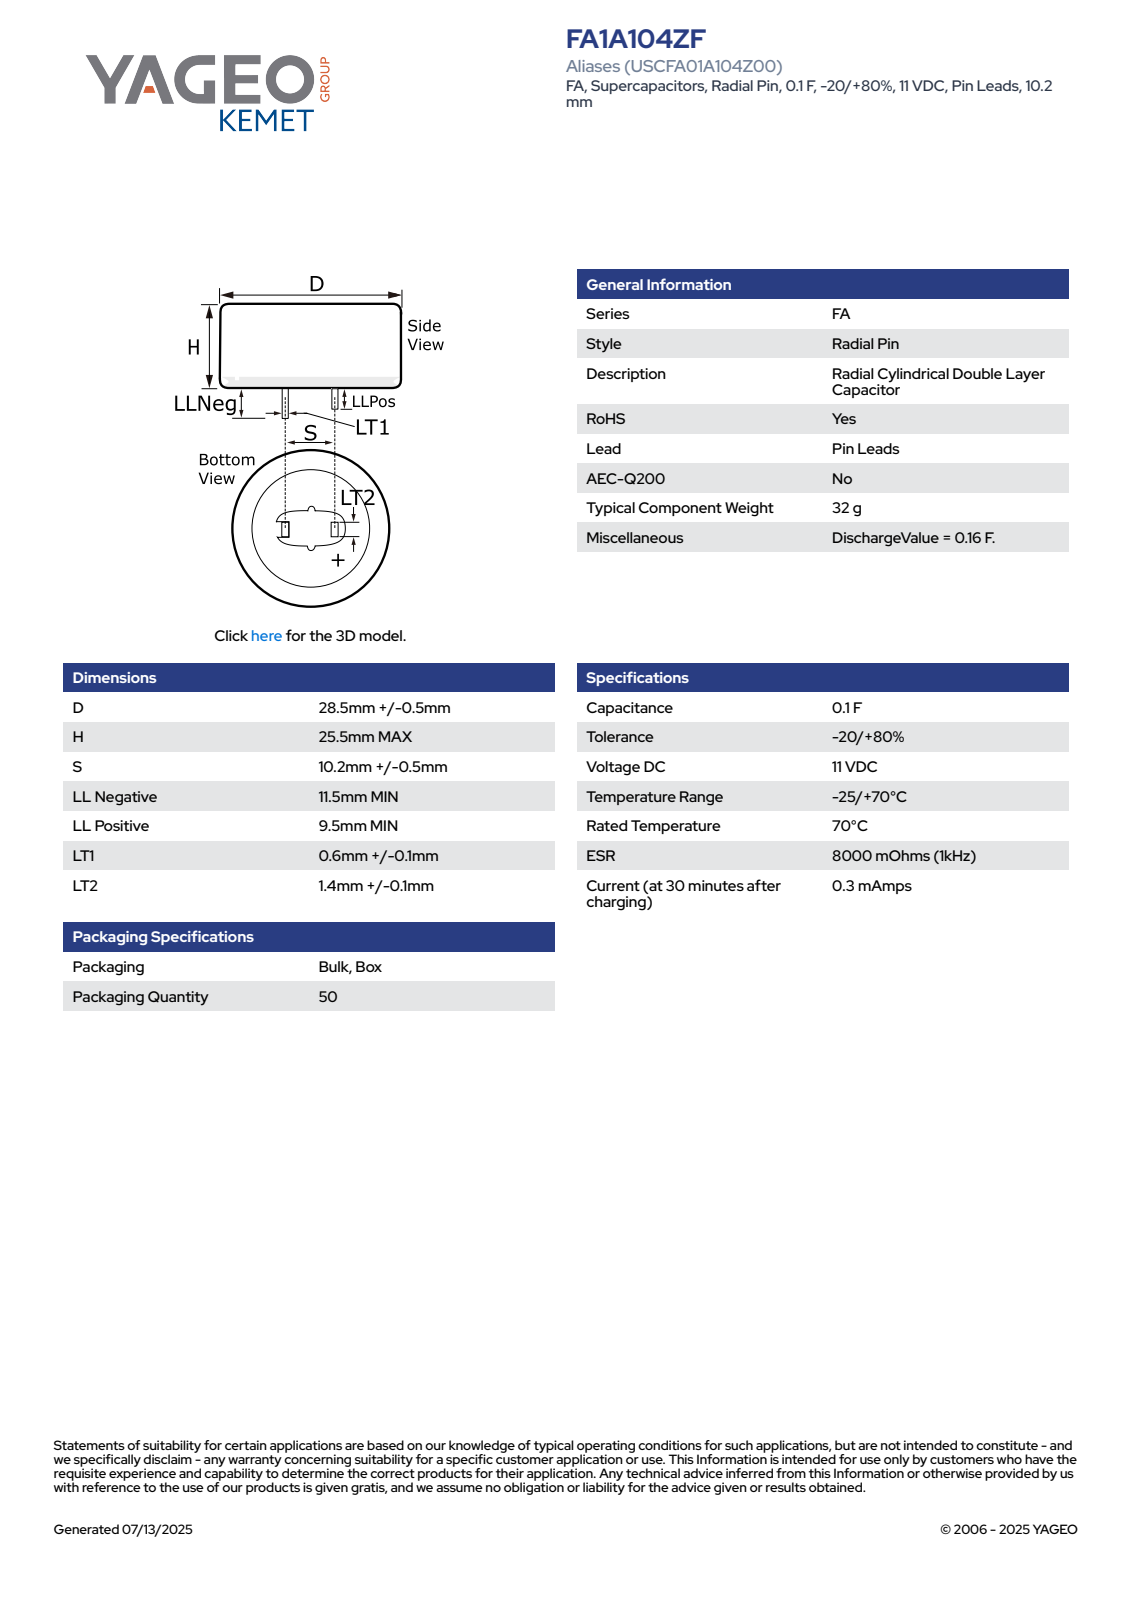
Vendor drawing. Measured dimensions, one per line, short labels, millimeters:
name: CDR_LPLLN_D29L25.5S10.2LLNEG11.5LLPOS9.5LT10.7LT21.5
written by: SolidWorks 2014 (AUTOMOTIVE_DESIGN)
unit: mm
bodies: 1 solid, 78 faces (70 planar, 4 cylindrical, 4 other)
size: 37 × 29 × 29
volume: 16 763 mm³; area: 3 606 mm²
bosses: 1× ⌀29
rounds: 1× R14.51
face distances: 25.5, 0.7, 10.2, 9.5, 1.5, 10.9, 25.49, 11.5, 36.99, 37
